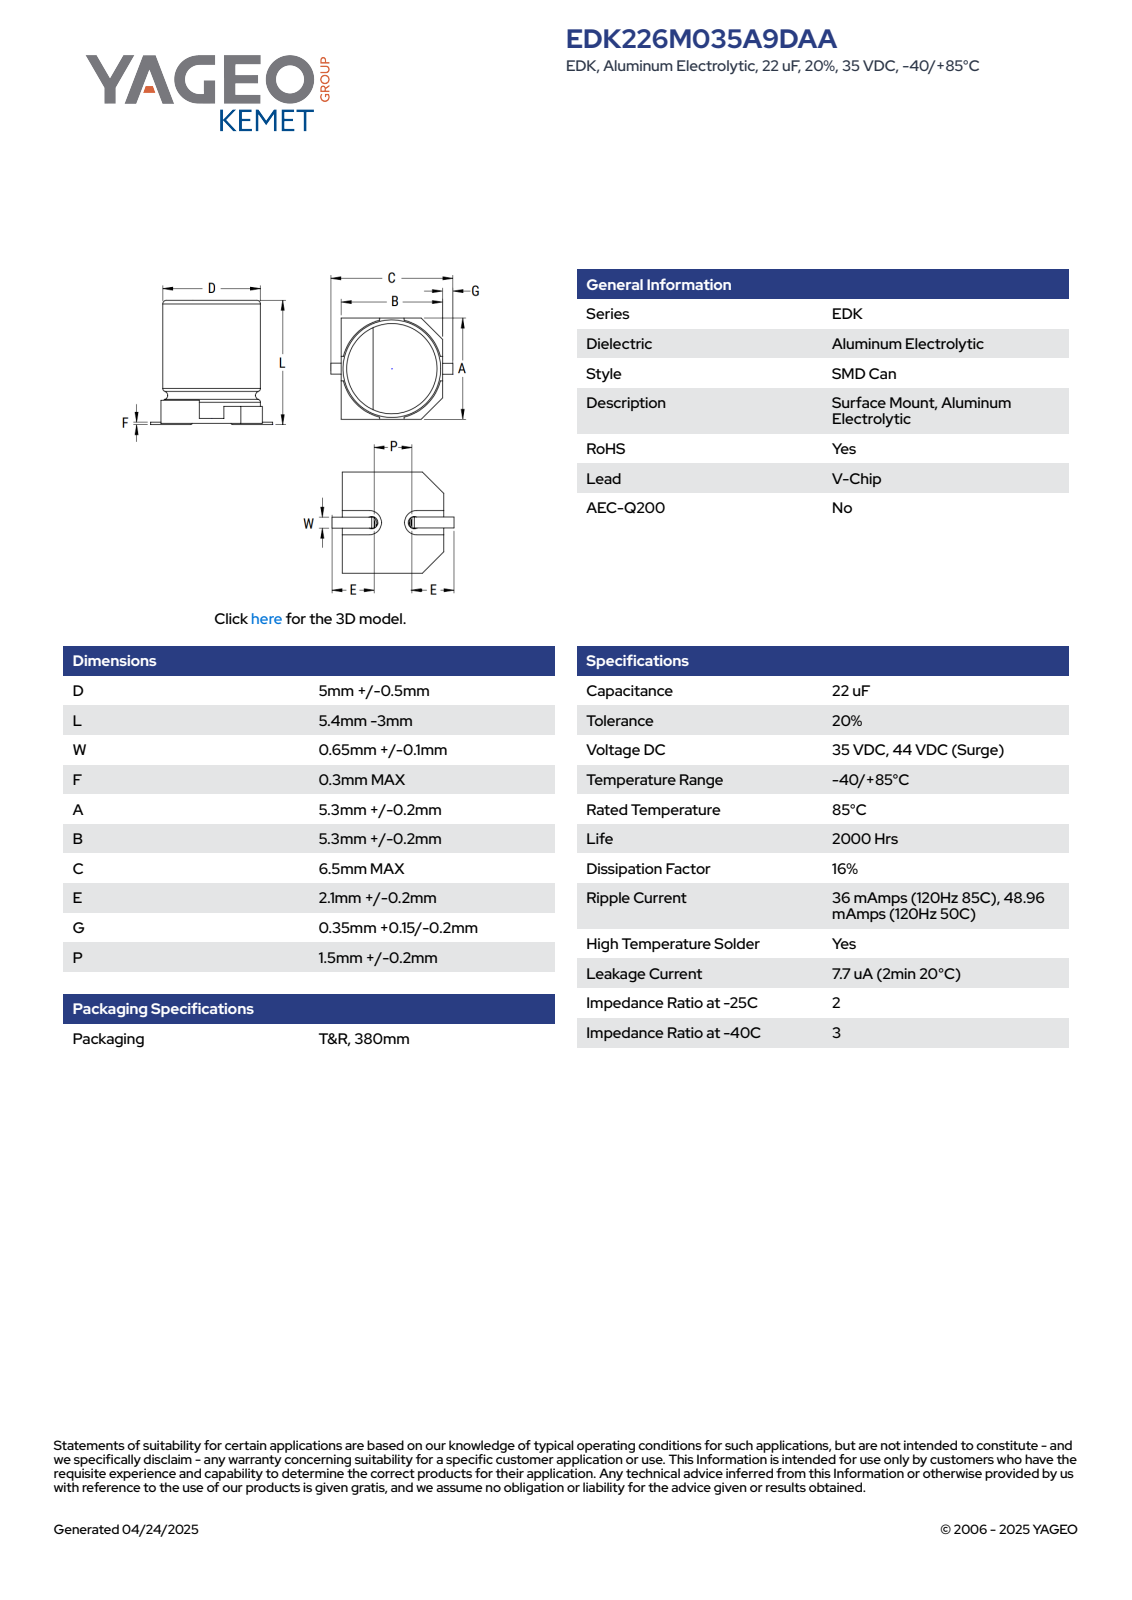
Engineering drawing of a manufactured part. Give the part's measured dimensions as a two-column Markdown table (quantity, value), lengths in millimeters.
| quantity | value |
| --- | --- |
| part name | CAC_S_5X5.4_D5.5L5.65W0.75F0.3A5.5B5.5C6.5E2.4P1.7 |
| STEP written by | SolidWorks 2014 (AUTOMOTIVE_DESIGN) |
| units | millimeters |
| bodies | 5 solids, 78 faces (61 planar, 11 cylindrical, 6 other) |
| overall size | 6.5 × 5.66 × 5.5 |
| volume | 122 mm³ |
| surface area | 217 mm² |
| round bosses / shafts (diameter × count) | 5.26 × 1 |
| partial cylindrical surfaces (radius × count) | 0.2 × 2, 2.18 × 1, 2.75 × 1 |
| main face-to-face distances | 5.35, 5.07, 5.36, 5.08, 5.5, 0.58, 5.65, 5.66, 1.71, 1.41 |
